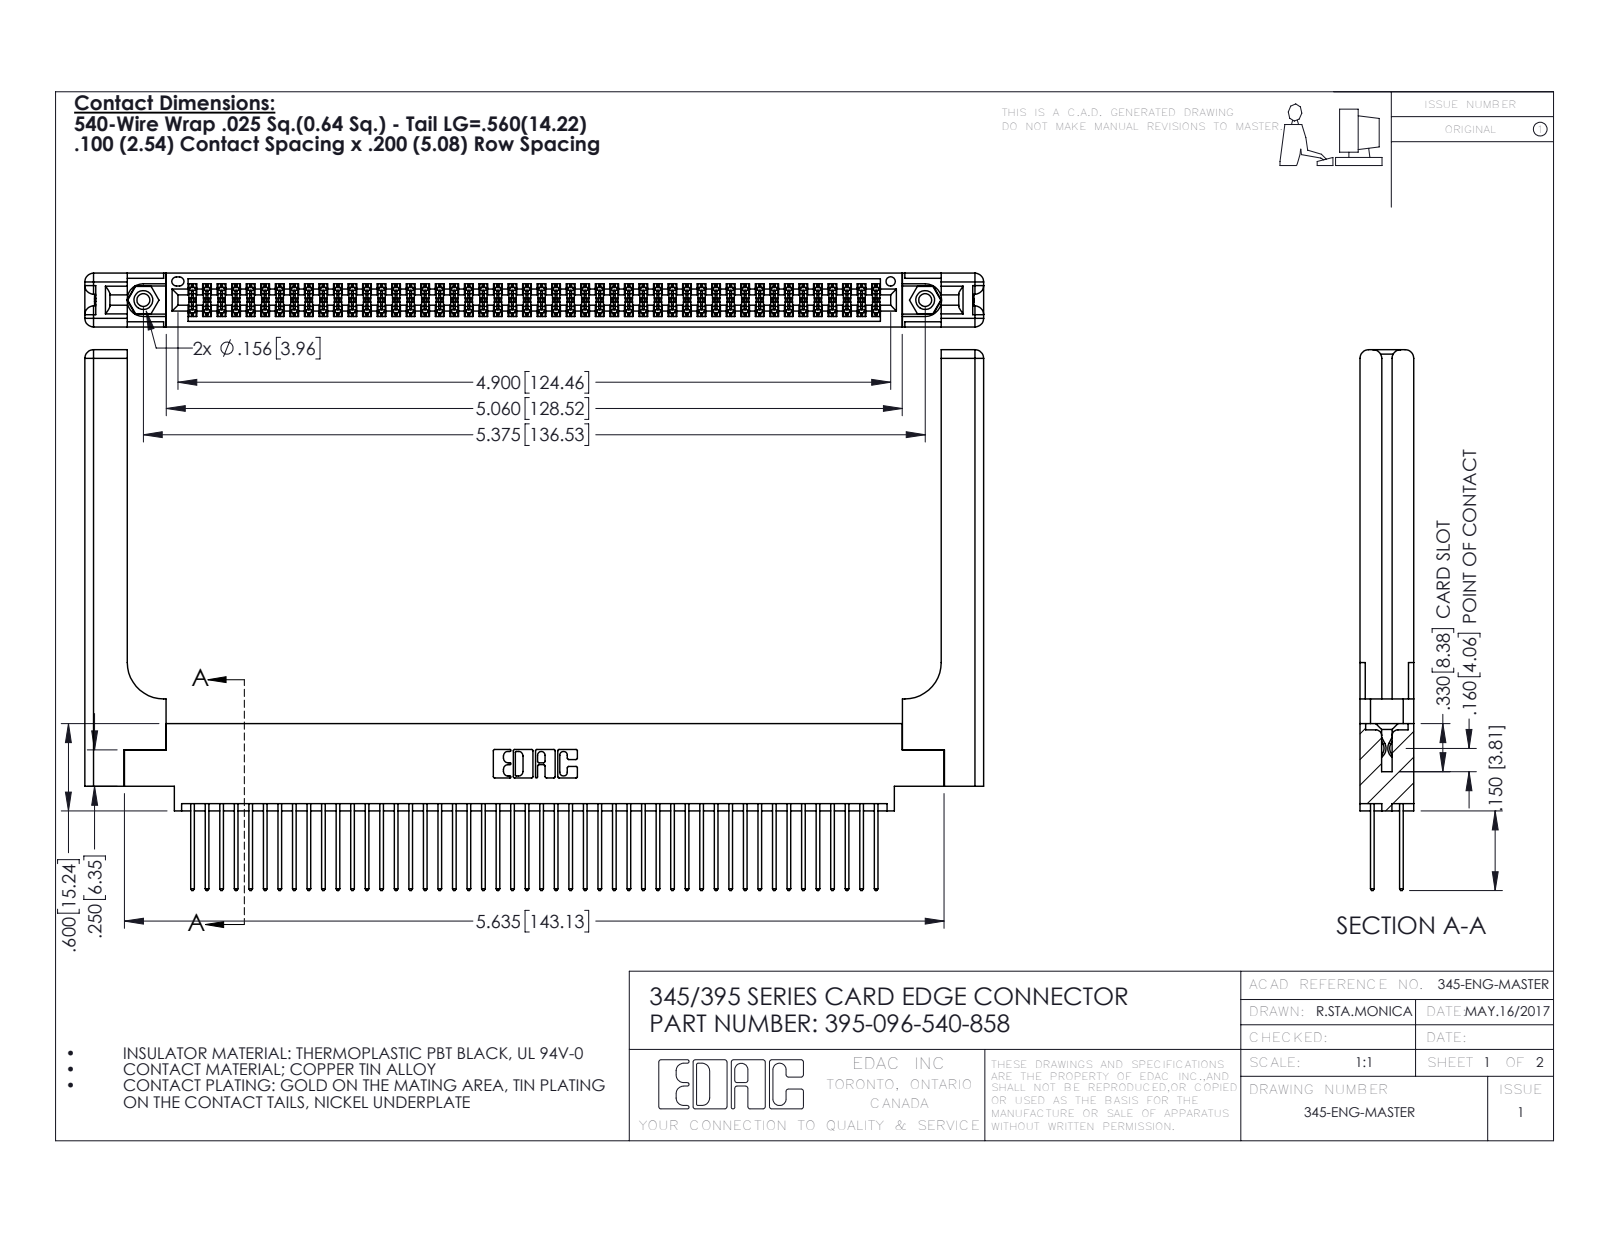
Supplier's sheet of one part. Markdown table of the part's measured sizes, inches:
| quantity | value |
| --- | --- |
| part name | 345 Part_0.170 Offset - 0.156 Dia-TH; 345-292-001_345-293-140; 345-220-058_345-220-058; 395-096-540-858 (+1 more) |
| STEP written by | SolidWorks 2016 (CONFIG_CONTROL_DESIGN) |
| units | inches |
| bodies | 101 solids, 5186 faces (3400 planar, 1726 cylindrical, 60 other) |
| overall size | 6.179 × 3.717 × 0.37 |
| volume | 1.466 in³ |
| surface area | 46.49 in² |
| round holes (diameter × count) | 0.089 × 2, 0.125 × 2, 0.156 × 2, 0.064 × 1 |
| round bosses / shafts (diameter × count) | 0.155 × 2 |
| partial cylindrical surfaces (radius × count) | 0.006 × 144, 0.01 × 96, 0.01 × 22, 0.06 × 16, 0.007 × 6, 0.031 × 6, 0.026 × 3, 0.014 × 2 |
| main face-to-face distances | 0.072, 0.298, 0.37, 0.098, 0.272, 0.025, 0.2, 0.225, 0.175, 0.148 |
| hole center spacings | 0.27, 5.139, 5.375 |
